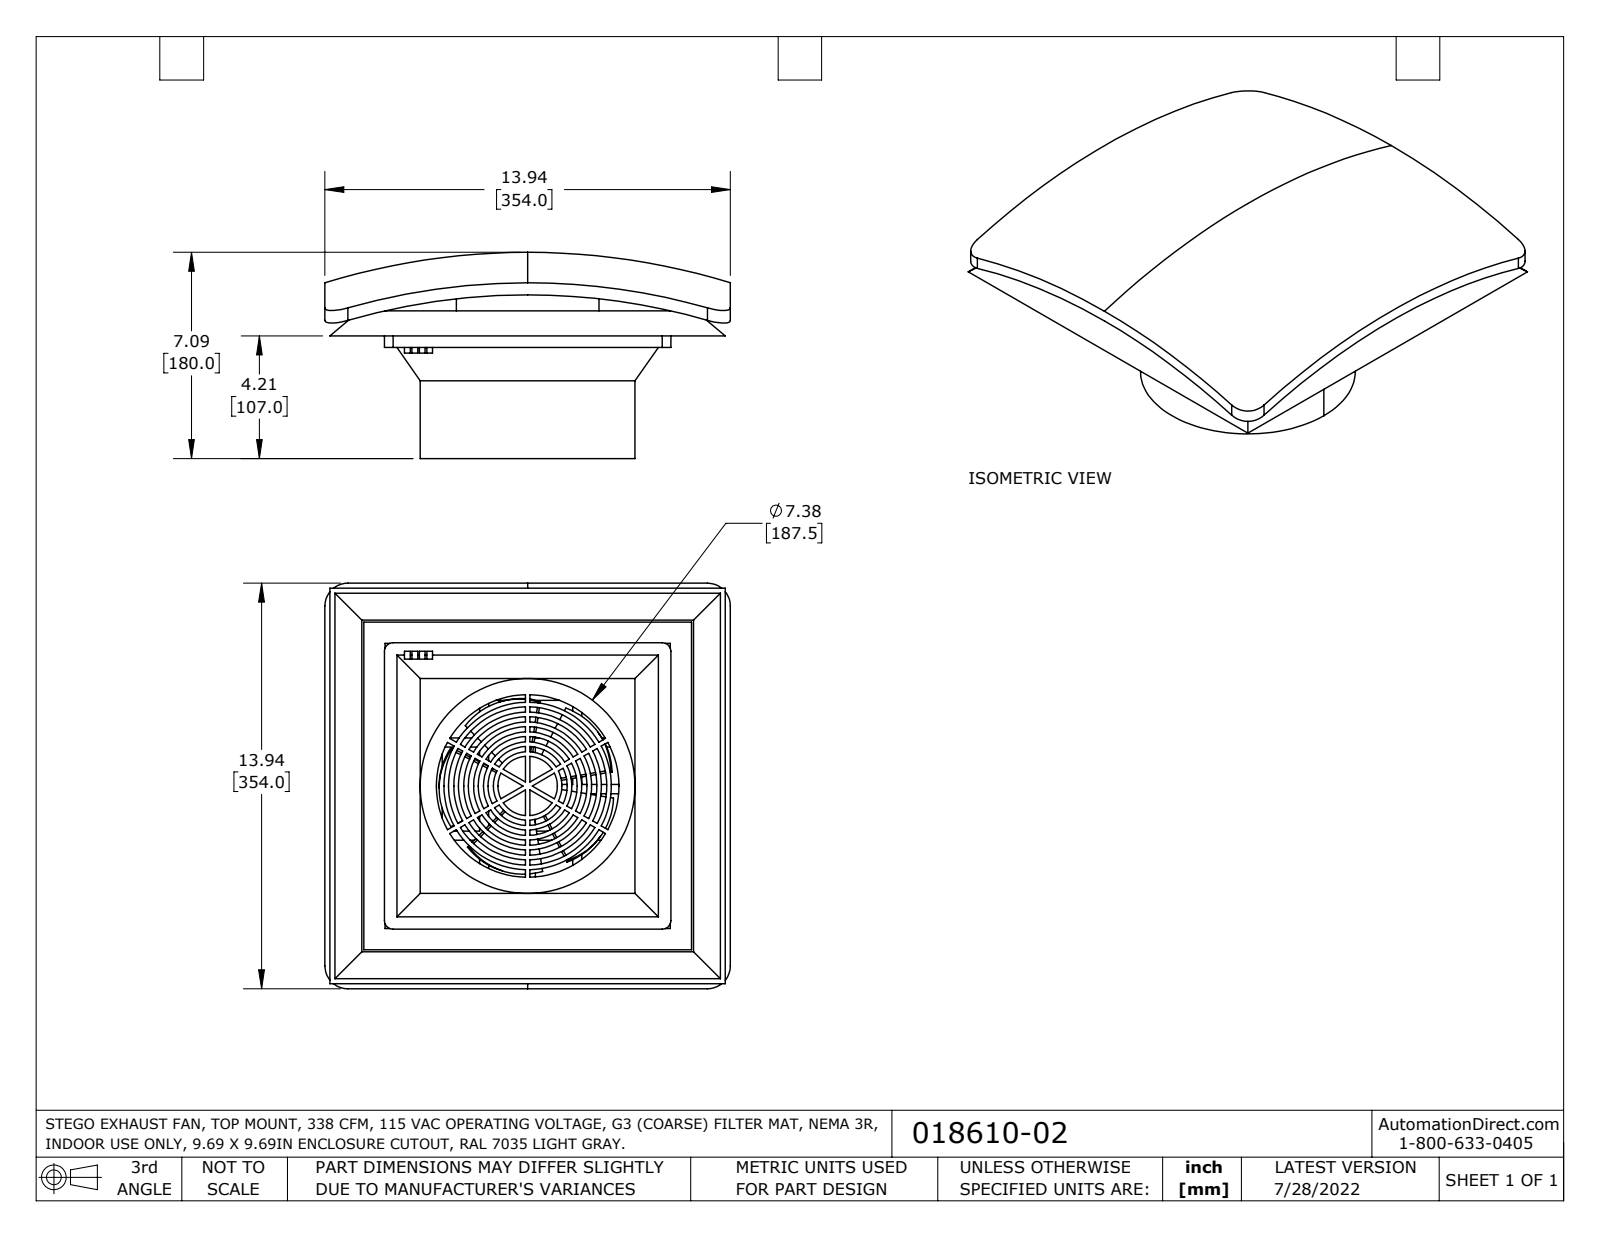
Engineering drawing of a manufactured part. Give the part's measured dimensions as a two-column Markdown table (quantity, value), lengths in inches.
| quantity | value |
| --- | --- |
| part name | 018610-02_Default |
| STEP written by | SolidWorks 2021 (CONFIG_CONTROL_DESIGN) |
| units | inches |
| bodies | 1 solid, 480 faces (361 planar, 115 cylindrical, 4 other) |
| overall size | 13.937 × 13.937 × 7.087 |
| volume | 286.6 in³ |
| surface area | 1 389 in² |
| round holes (diameter × count) | 2.039 × 1, 2.718 × 1, 3.398 × 1, 4.078 × 1, 4.758 × 1, 5.437 × 1, 6.275 × 1 |
| round bosses / shafts (diameter × count) | 7.382 × 1, 5.752 × 1, 5.073 × 1, 4.393 × 1, 3.713 × 1, 3.033 × 1, 2.354 × 1, 2.196 × 1 |
| partial cylindrical surfaces (radius × count) | 3.043 × 5, 0.295 × 4, 0.787 × 4 |
| main face-to-face distances | 0.431, 0.862, 0.109, 0.157, 0.172, 0.259, 0.69, 0.728, 10.531, 1.601 |
